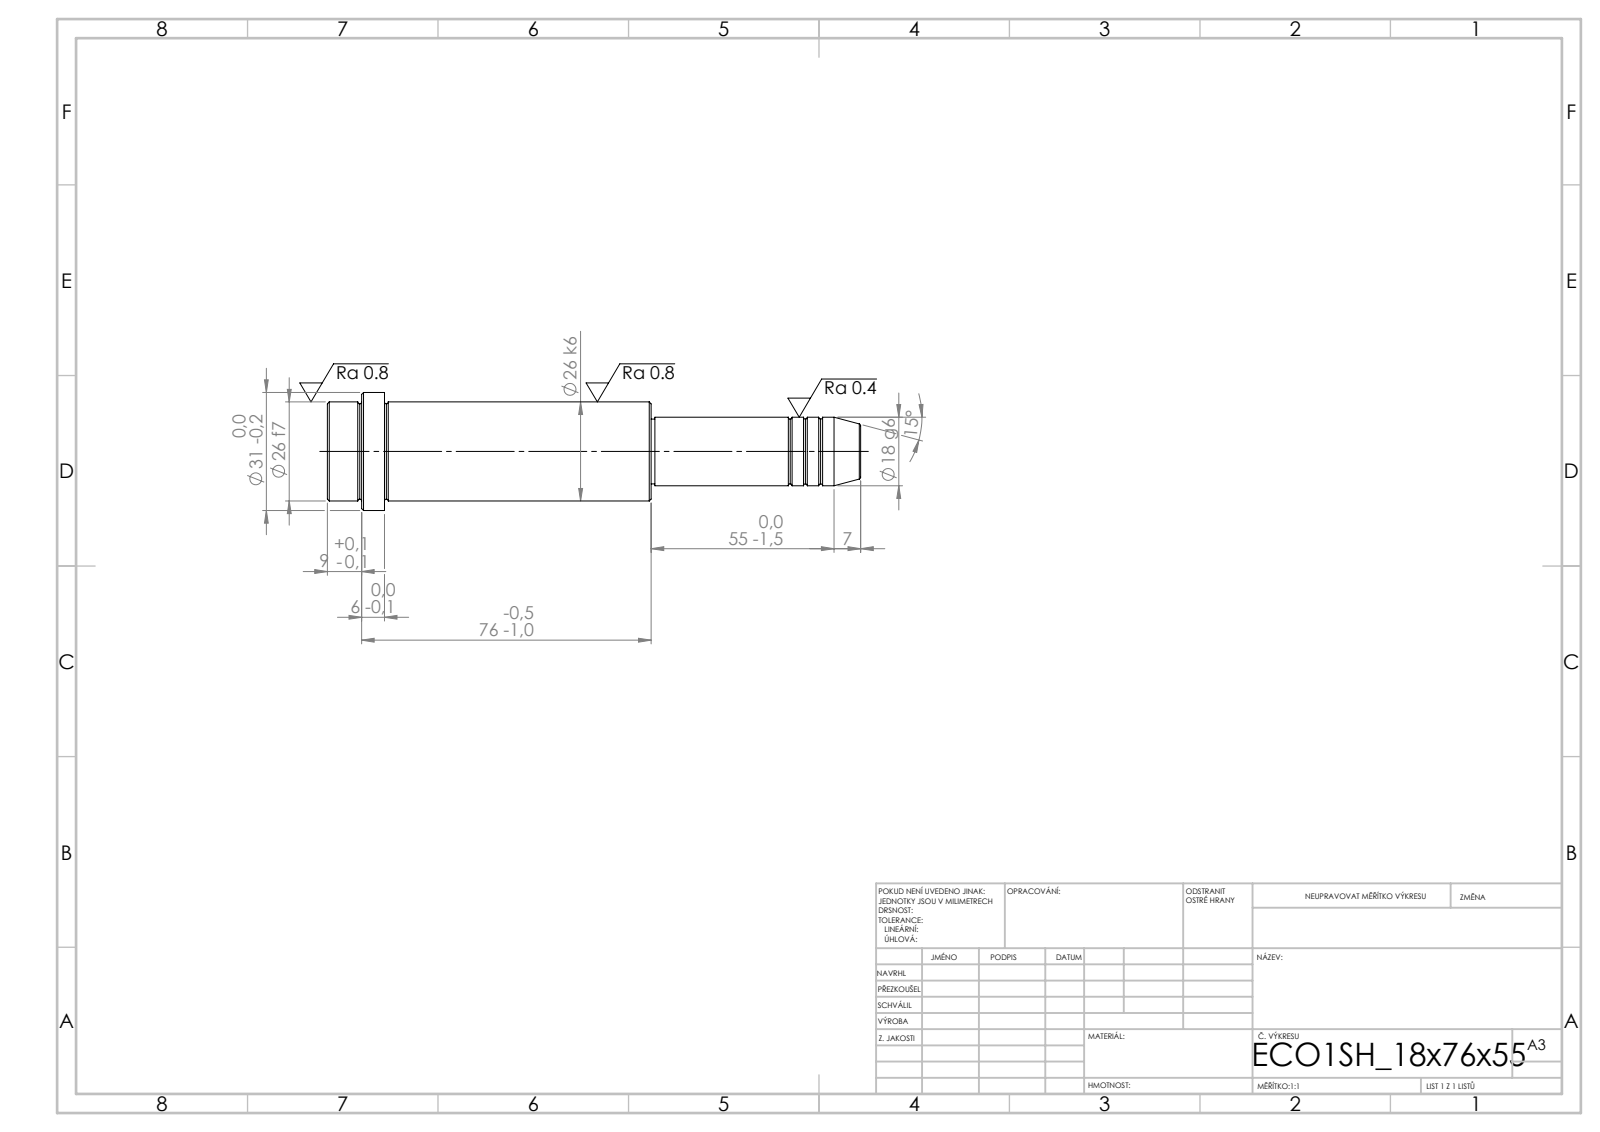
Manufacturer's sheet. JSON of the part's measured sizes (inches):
{"step_written_by": "SolidWorks 2019 (CONFIG_CONTROL_DESIGN)", "units": "inches", "bodies": {"solids": 1, "faces": 52, "planar": 6, "cylindrical": 16, "other": 30}, "overall_size": [5.512, 1.22, 1.22], "volume_in3": 3.657, "surface_area_in2": 18.1, "round_bosses_or_shafts": [[1.22, 1], [1.024, 1], [0.709, 1], [0.669, 1]], "face_to_face_distances": [3.346, 2.756, 0.591, 2.992, 0.236, 0.354, 2.165, 4.921, 5.157, 5.512]}
